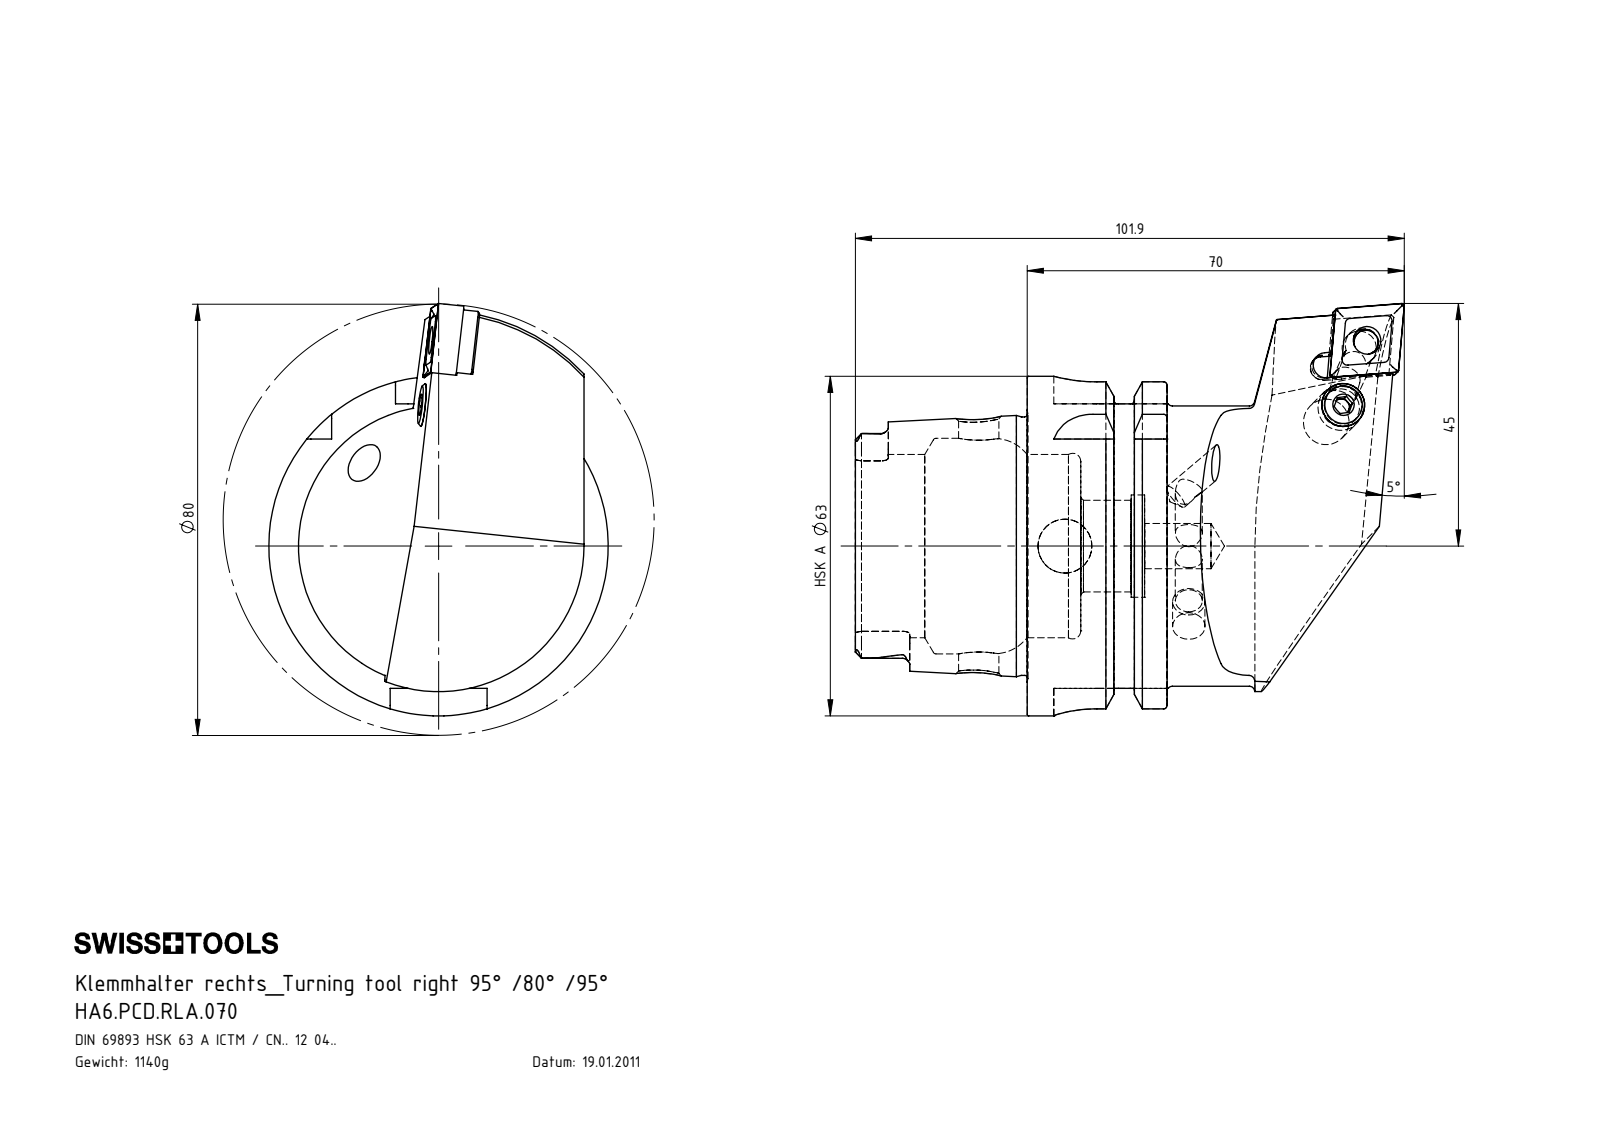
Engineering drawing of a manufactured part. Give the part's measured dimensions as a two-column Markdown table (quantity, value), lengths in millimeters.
| quantity | value |
| --- | --- |
| part name | HA6-PCD.RLA.070; CNMG120404; WCD-ER2.101.003_A; WCD (+4 more) |
| STEP written by | SolidWorks 2012 (CONFIG_CONTROL_DESIGN) |
| units | millimeters |
| bodies | 7 solids, 371 faces (118 planar, 105 cylindrical, 148 other) |
| overall size | 101.9 × 76.5 × 63 |
| volume | 144 720 mm³ |
| surface area | 32 870 mm² |
| round holes (diameter × count) | 5 × 3, 8.4 × 2, 5.16 × 1, 6 × 1, 6.4 × 1, 7 × 1, 7.5 × 1, 10 × 1, 17 × 1, 19 × 1, 34 × 1, 40 × 1 |
| round bosses / shafts (diameter × count) | 63 × 1, 54.95 × 1, 52 × 1, 47.94 × 1, 8 × 1, 7.9 × 1, 6.4 × 1, 6 × 1 |
| partial cylindrical surfaces (radius × count) | 1.4 × 6, 0.4 × 4, 1 × 4, 8 × 4, 2.5 × 2, 2.82 × 2, 2.88 × 2, 2.1 × 1 |
| main face-to-face distances | 25.95, 16, 9.95, 31.9, 41.85, 57.85, 52.8, 21.8, 11.85, 4.46 |
| hole center spacings | 12.8, 12.85 |
